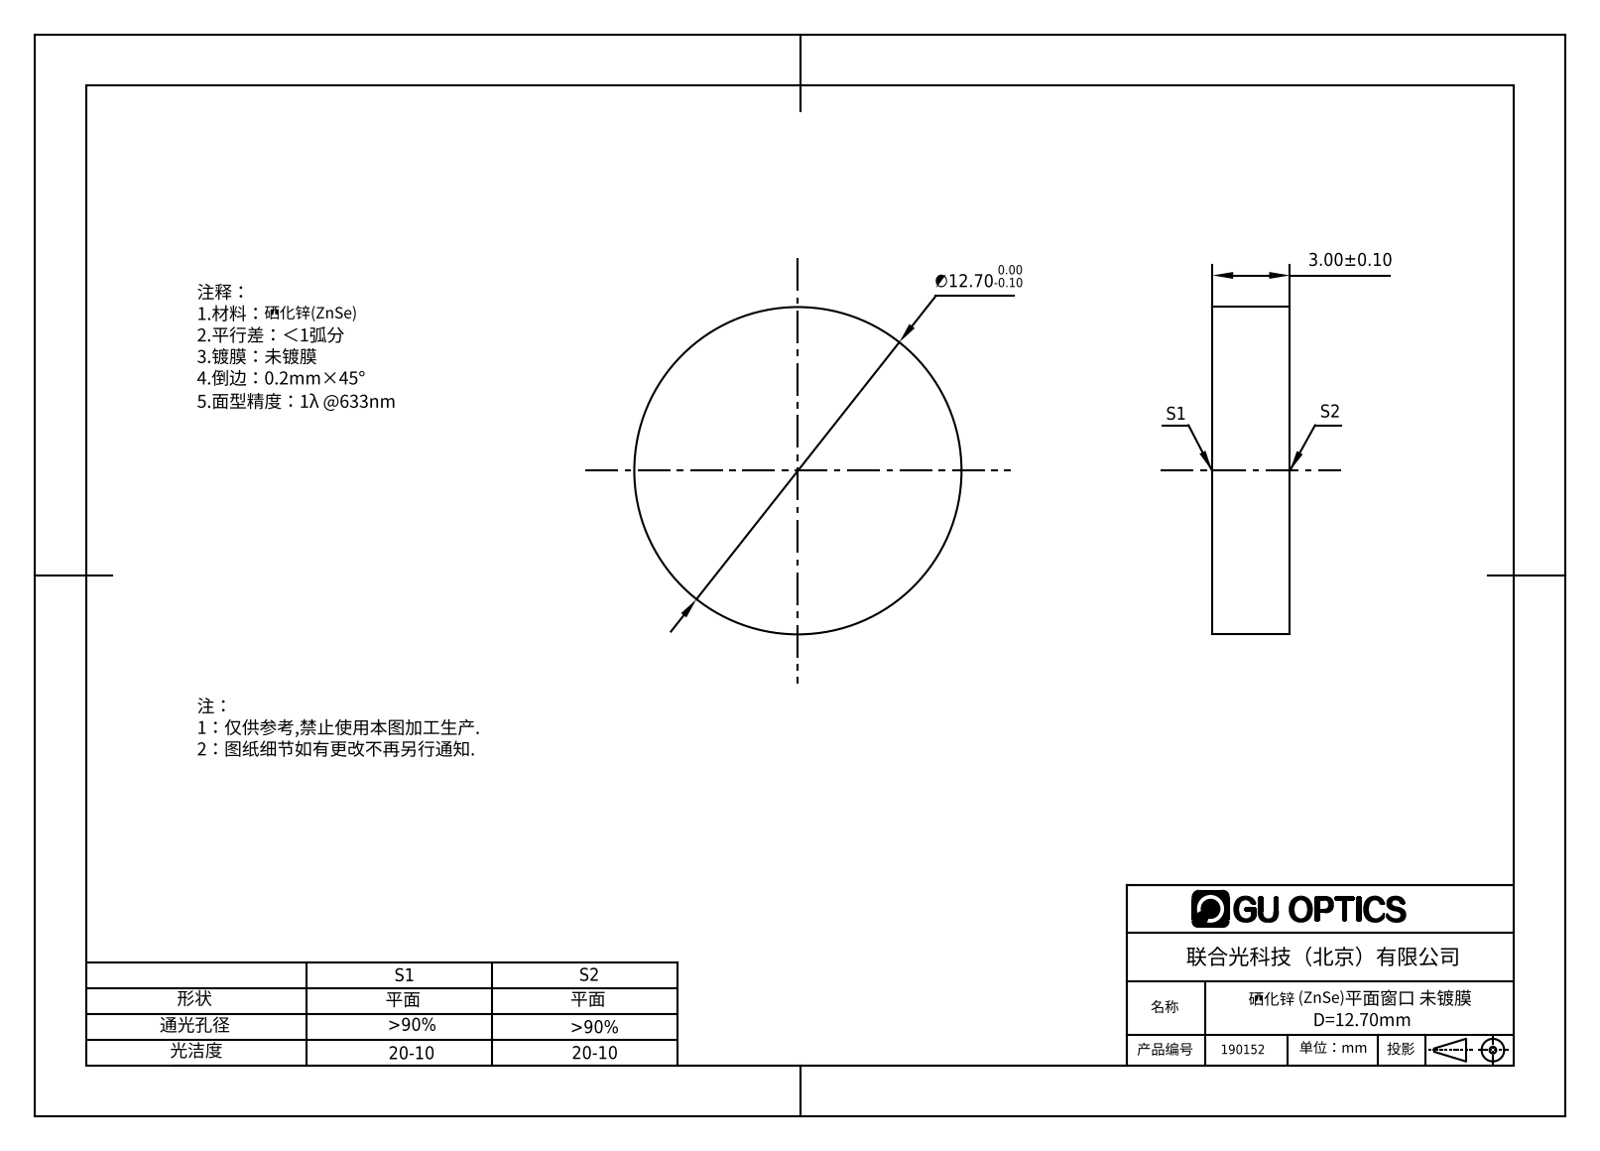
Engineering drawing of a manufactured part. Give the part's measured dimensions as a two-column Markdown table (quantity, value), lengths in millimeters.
| quantity | value |
| --- | --- |
| part name | 190152 |
| STEP written by | SolidWorks 2016 (AUTOMOTIVE_DESIGN) |
| units | millimeters |
| bodies | 1 solid, 4 faces (2 planar, 2 cylindrical, 0 other) |
| overall size | 12.7 × 12.7 × 3 |
| volume | 380 mm³ |
| surface area | 373 mm² |
| round bosses / shafts (diameter × count) | 12.7 × 1 |
| main face-to-face distances | 3 |
